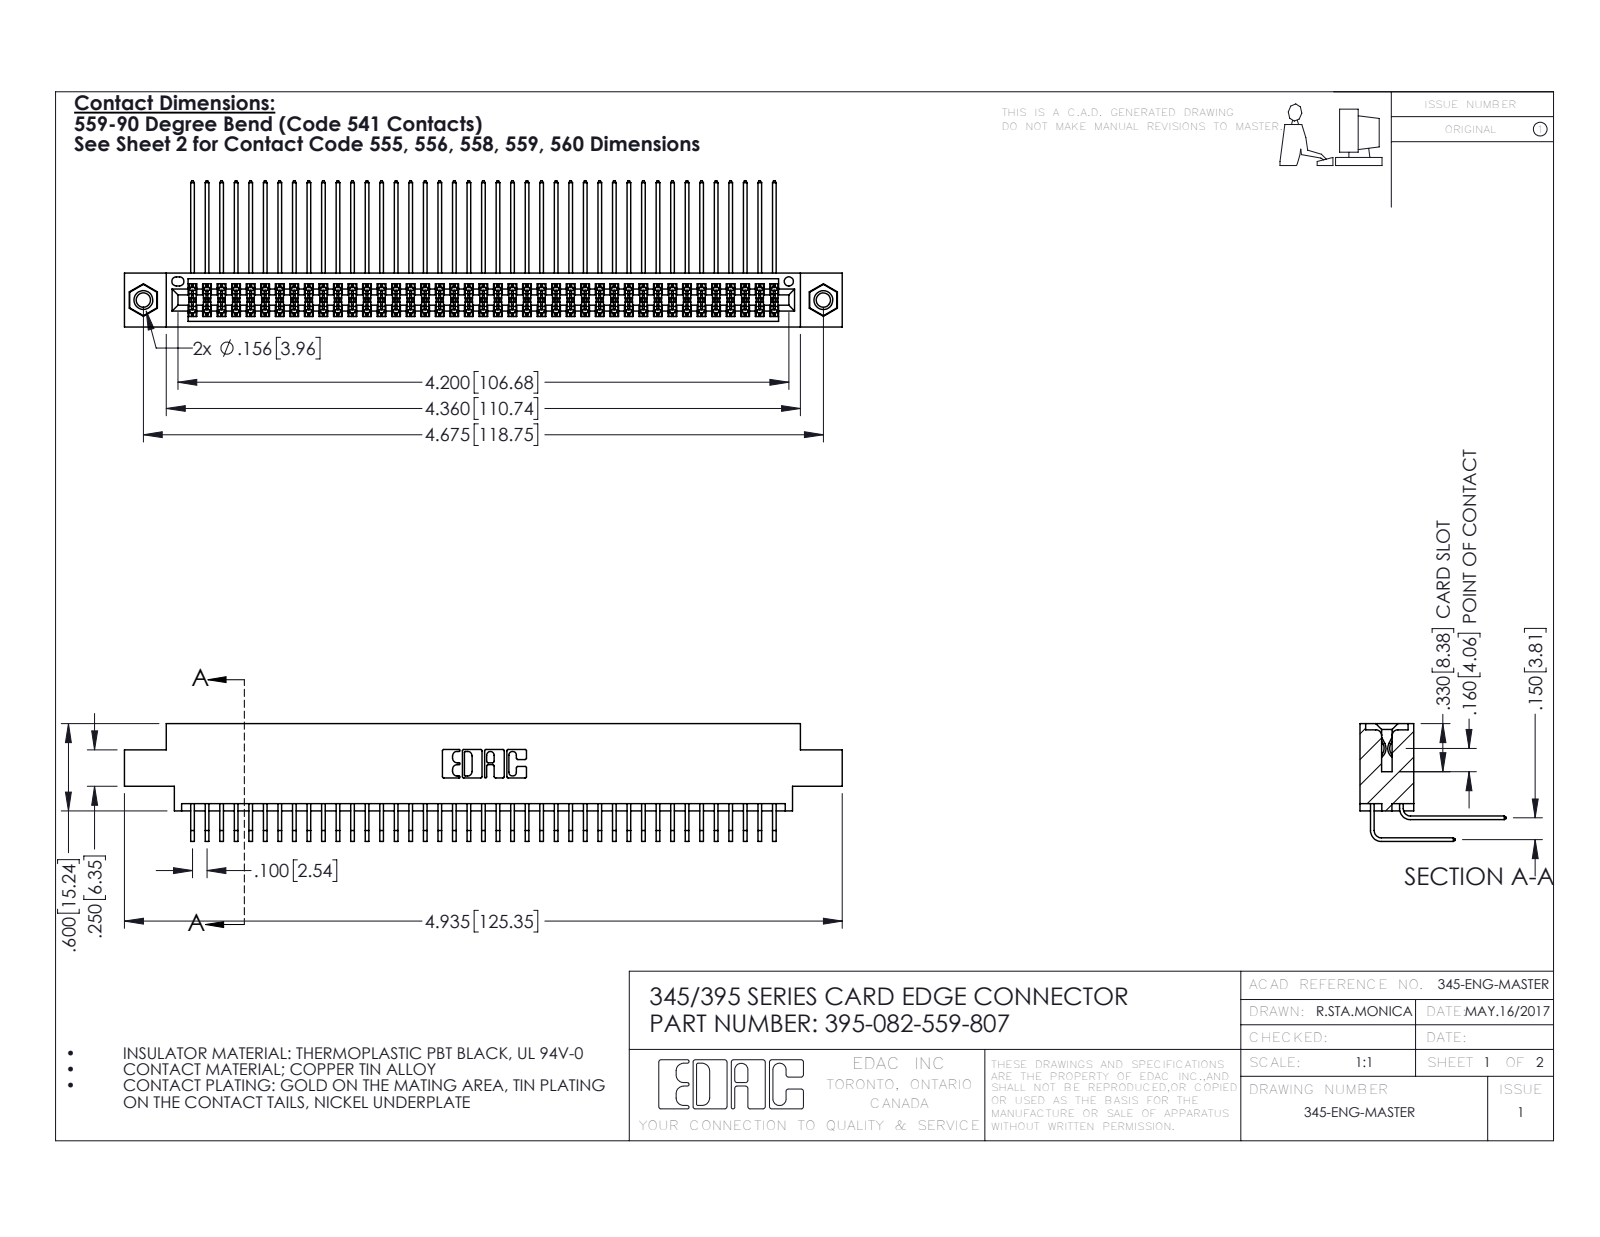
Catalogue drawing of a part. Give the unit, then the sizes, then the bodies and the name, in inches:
Units: inches
Overall size (bounding box): 4.935 × 1.005 × 0.809
Round holes (diameter × count): ⌀0.098 ×2, ⌀0.125 ×2, ⌀0.156 ×2, ⌀0.064 ×1
Round bosses / shafts (diameter × count): ⌀0.155 ×2
Partial cylindrical surfaces — rounded edges, fillets, slot ends (radius × count): R0.006 ×123, R0.01 ×22, R0.007 ×6, R0.031 ×6, R0.026 ×3, R0.014 ×2, R0.019 ×2, R0.022 ×2
Main face-to-face distances: 0.072, 0.298, 0.37, 0.2, 0.098, 0.272, 0.025, 0.225, 0.175, 0.15
Hole centre spacings: 0.27, 4.439, 4.675
Volume: 0.764 in³ · Surface area: 32.35 in²
Bodies: 85 solids, 4454 faces (2986 planar, 1452 cylindrical, 16 other)
Part name (STEP PRODUCT): 345-292-001_558 559 Tail - 1; 345-250-001_345-250-005-103; 395-082-559-807; 345-292-001_559 Tail - 2 (+1 more)
STEP written by: SolidWorks 2016 (CONFIG_CONTROL_DESIGN)
